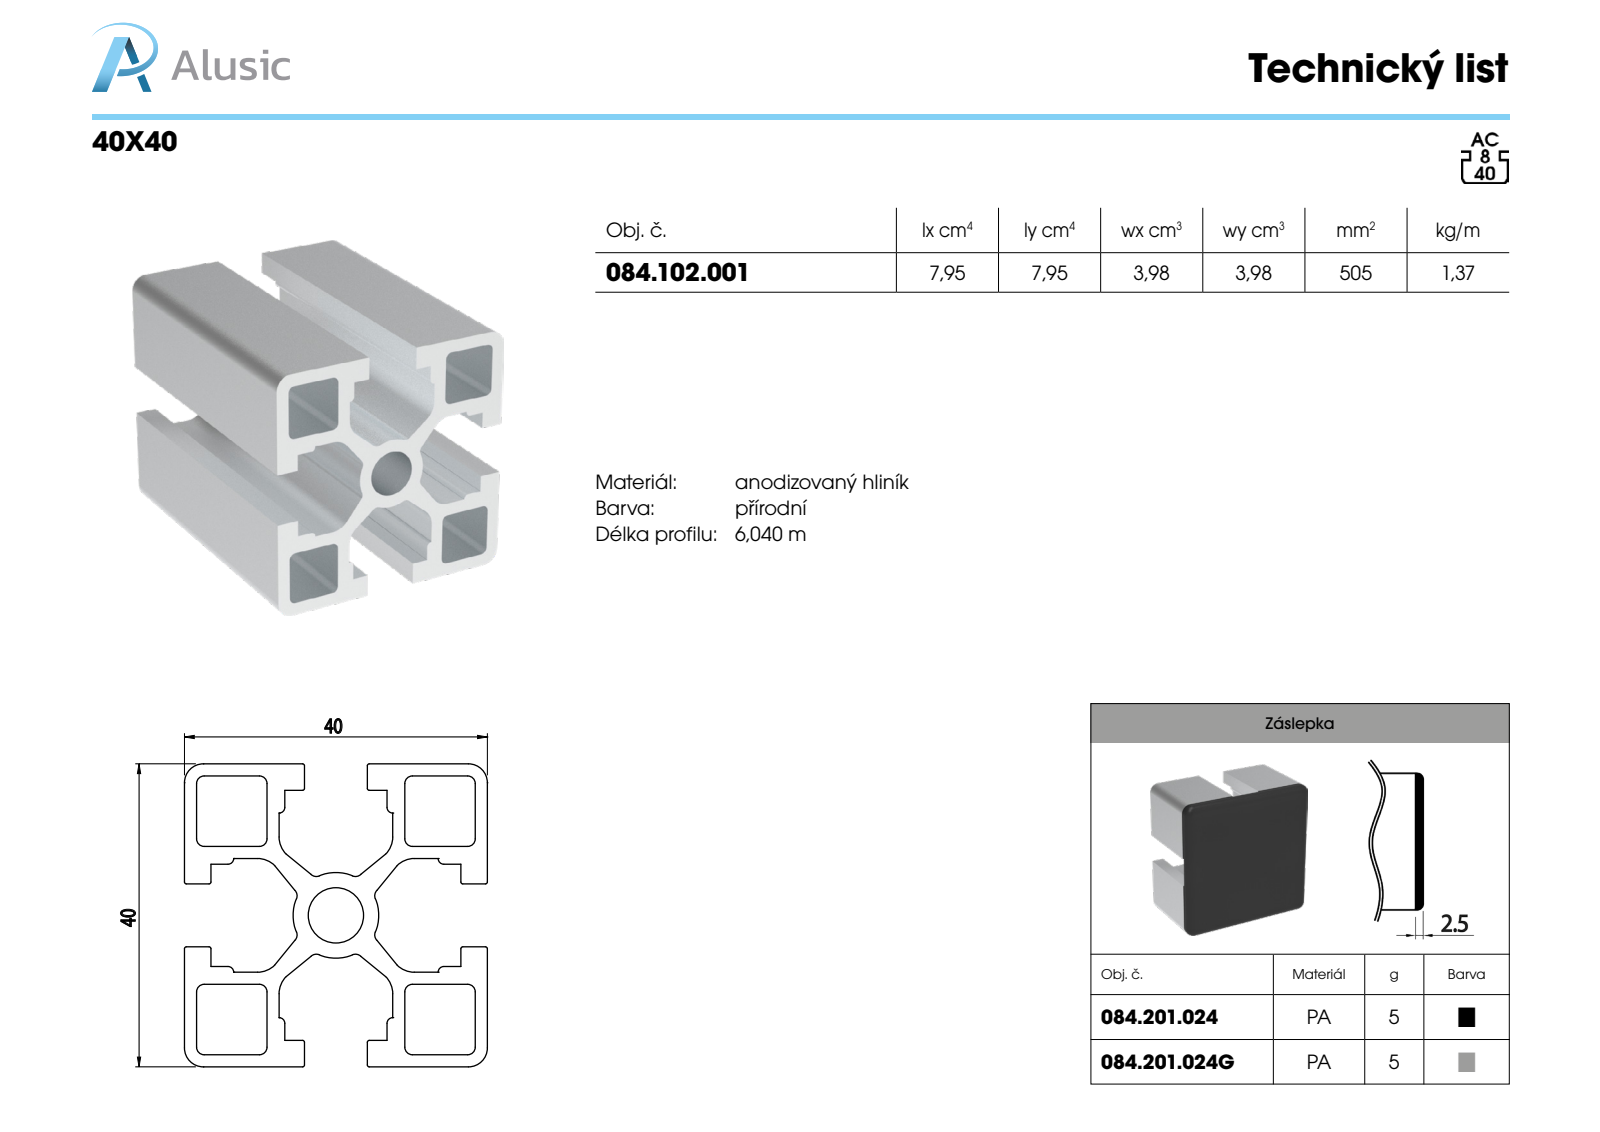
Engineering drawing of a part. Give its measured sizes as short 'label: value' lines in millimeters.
name: 084.102.001
written by: SolidWorks 2011 (CONFIG_CONTROL_DESIGN)
unit: mm
bodies: 1 solid, 127 faces (74 planar, 53 cylindrical, 0 other)
size: 100 × 40 × 40
volume: 56 375 mm³; area: 46 865 mm²
holes: 1× ⌀7.3
rounds: 24× R1, 8× R0.7, 8× R3.2, 4× R2.5, 1× R5.65
face distances: 10.5, 27.5, 2, 40, 29.5, 38, 8.5, 15.85, 24.15, 13.85
